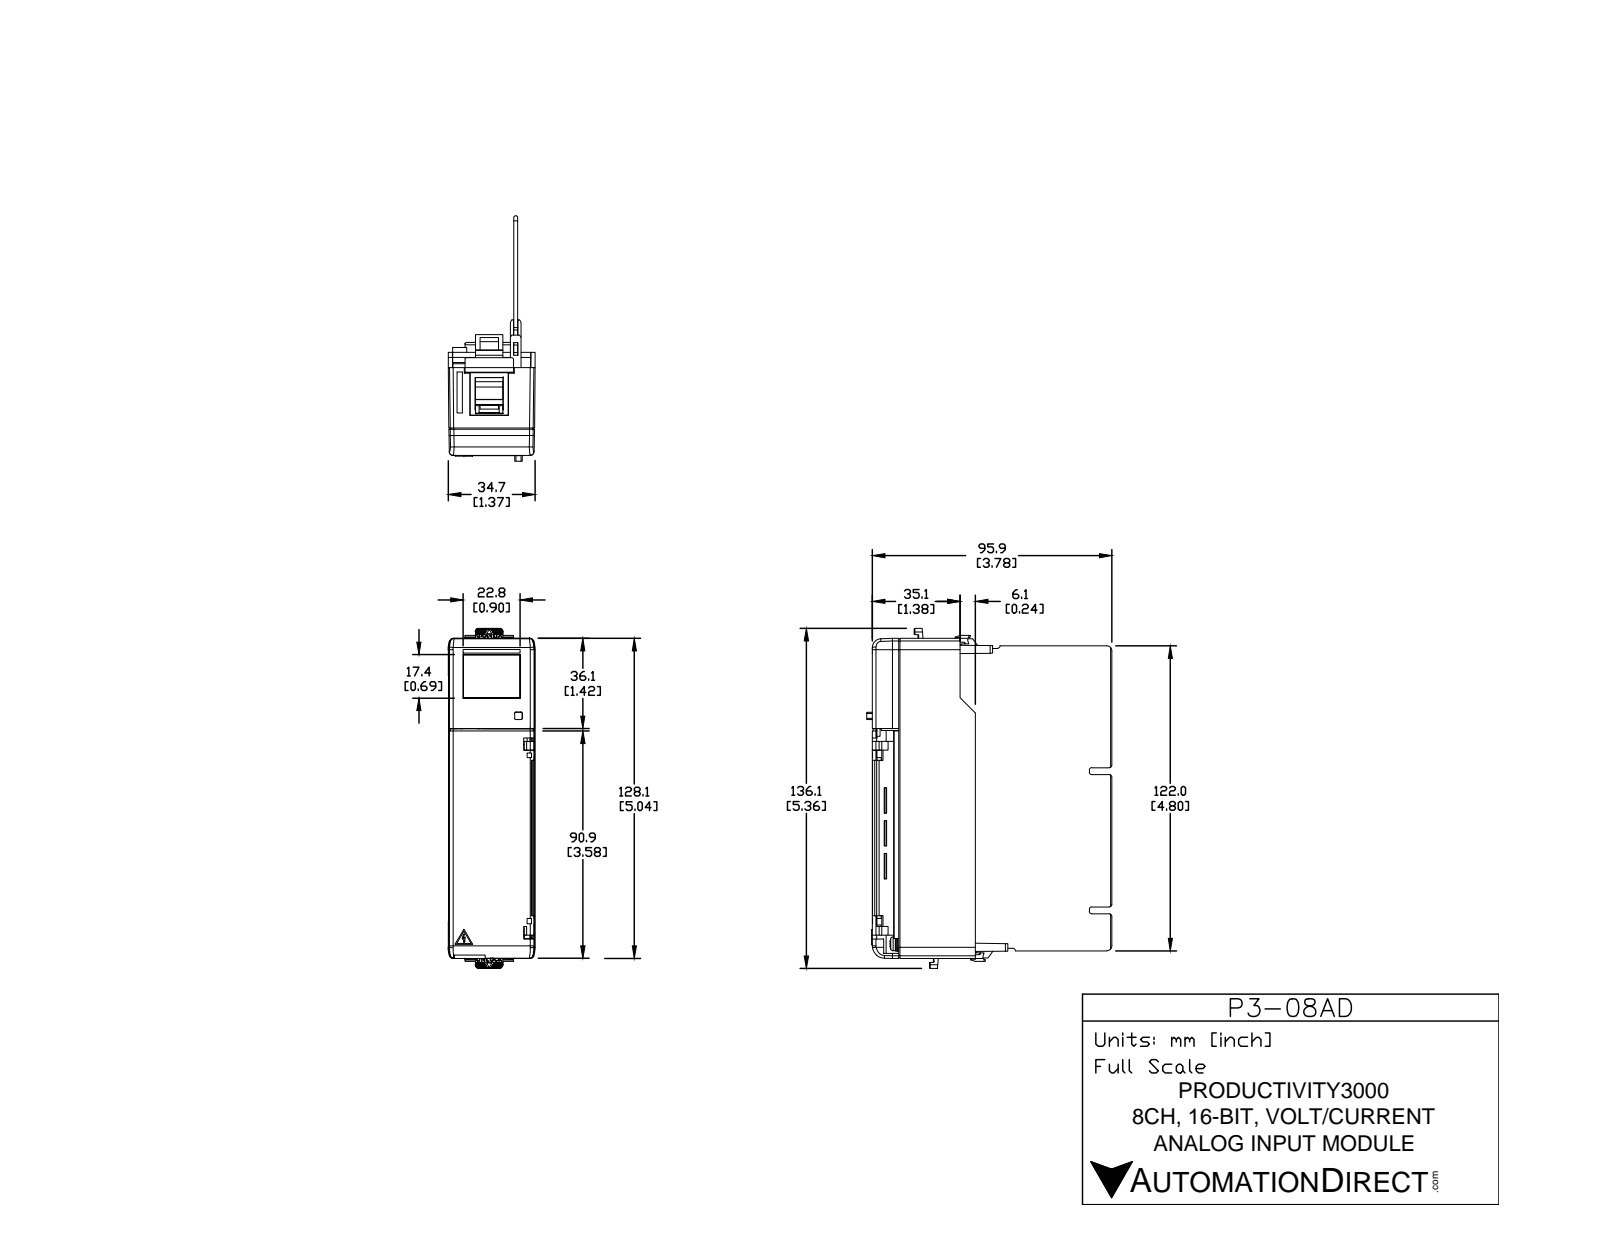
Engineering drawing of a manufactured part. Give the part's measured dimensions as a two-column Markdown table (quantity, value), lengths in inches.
| quantity | value |
| --- | --- |
| part name | P3-08AD |
| STEP written by | SolidWorks 2009 (CONFIG_CONTROL_DESIGN) |
| units | inches |
| bodies | 1 solid, 3823 faces (2833 planar, 744 cylindrical, 246 other) |
| overall size | 5.357 × 3.865 × 1.37 |
| volume | 6.185 in³ |
| surface area | 116.8 in² |
| round holes (diameter × count) | 0.126 × 22, 0.197 × 2, 0.071 × 1 |
| round bosses / shafts (diameter × count) | 0.217 × 22, 0.118 × 22, 0.094 × 20, 0.22 × 2, 0.087 × 2, 0.079 × 2, 0.059 × 1 |
| partial cylindrical surfaces (radius × count) | 0.02 × 95, 0.039 × 33, 0.012 × 29, 0.066 × 22, 0.059 × 13, 0.079 × 6, 0.008 × 5, 0.004 × 4 |
| main face-to-face distances | 0.063, 0.067, 1.111, 1.044, 1.282, 0.874, 0.087, 0.311, 0.268, 0.209 |
| hole center spacings | 0.342, 0.3, 0.545, 0.6, 0.811, 0.9, 1.094, 1.2 |
